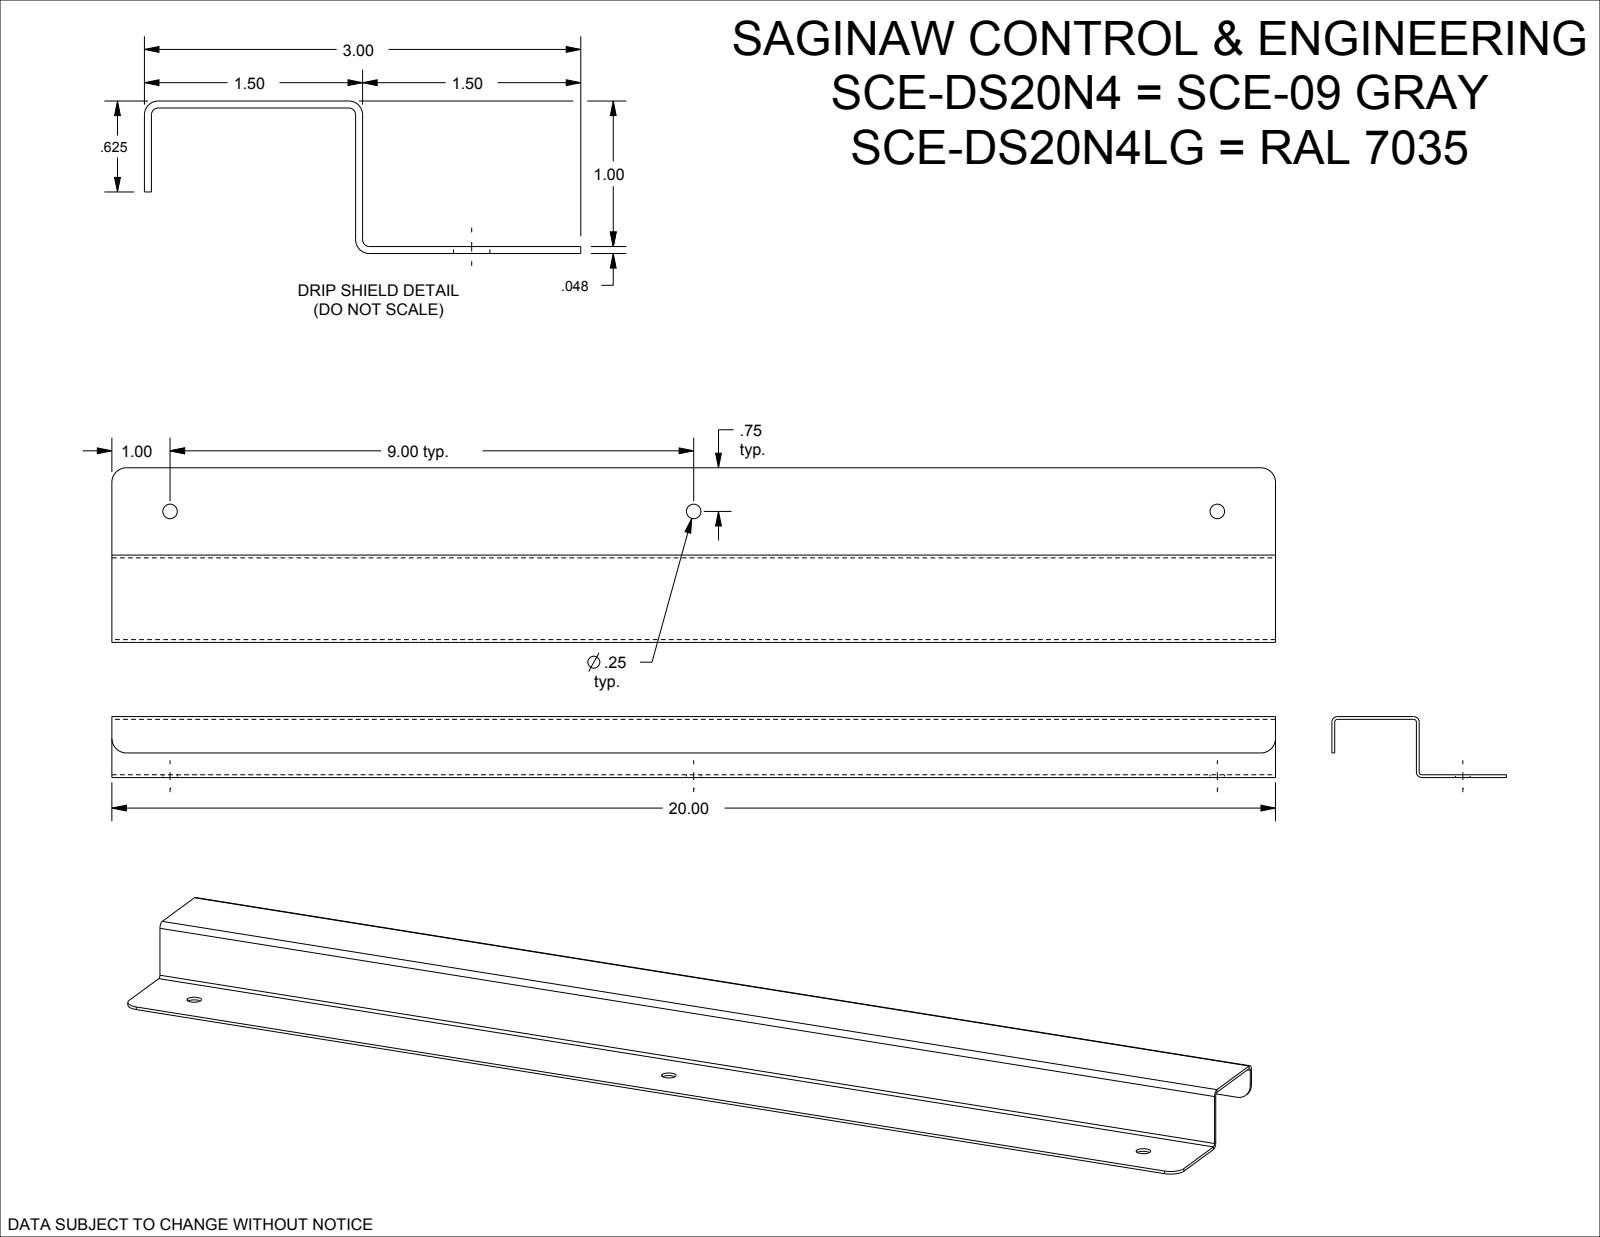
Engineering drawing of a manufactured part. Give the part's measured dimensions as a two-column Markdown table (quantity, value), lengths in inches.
| quantity | value |
| --- | --- |
| part name | SCE-DS20N4LG |
| STEP written by | SolidWorks 2019 (CONFIG_CONTROL_DESIGN) |
| units | inches |
| bodies | 1 solid, 25 faces (12 planar, 13 cylindrical, 0 other) |
| overall size | 20 × 3 × 1.048 |
| volume | 4.297 in³ |
| surface area | 181.5 in² |
| round holes (diameter × count) | 0.25 × 3 |
| partial cylindrical surfaces (radius × count) | 0.25 × 4, 0.047 × 3, 0.095 × 3 |
| main face-to-face distances | 0.048, 1, 0.952, 1.048, 1.452, 1.5, 1.404, 0.423, 0.375, 0.577 |
| hole center spacings | 9, 18 |
